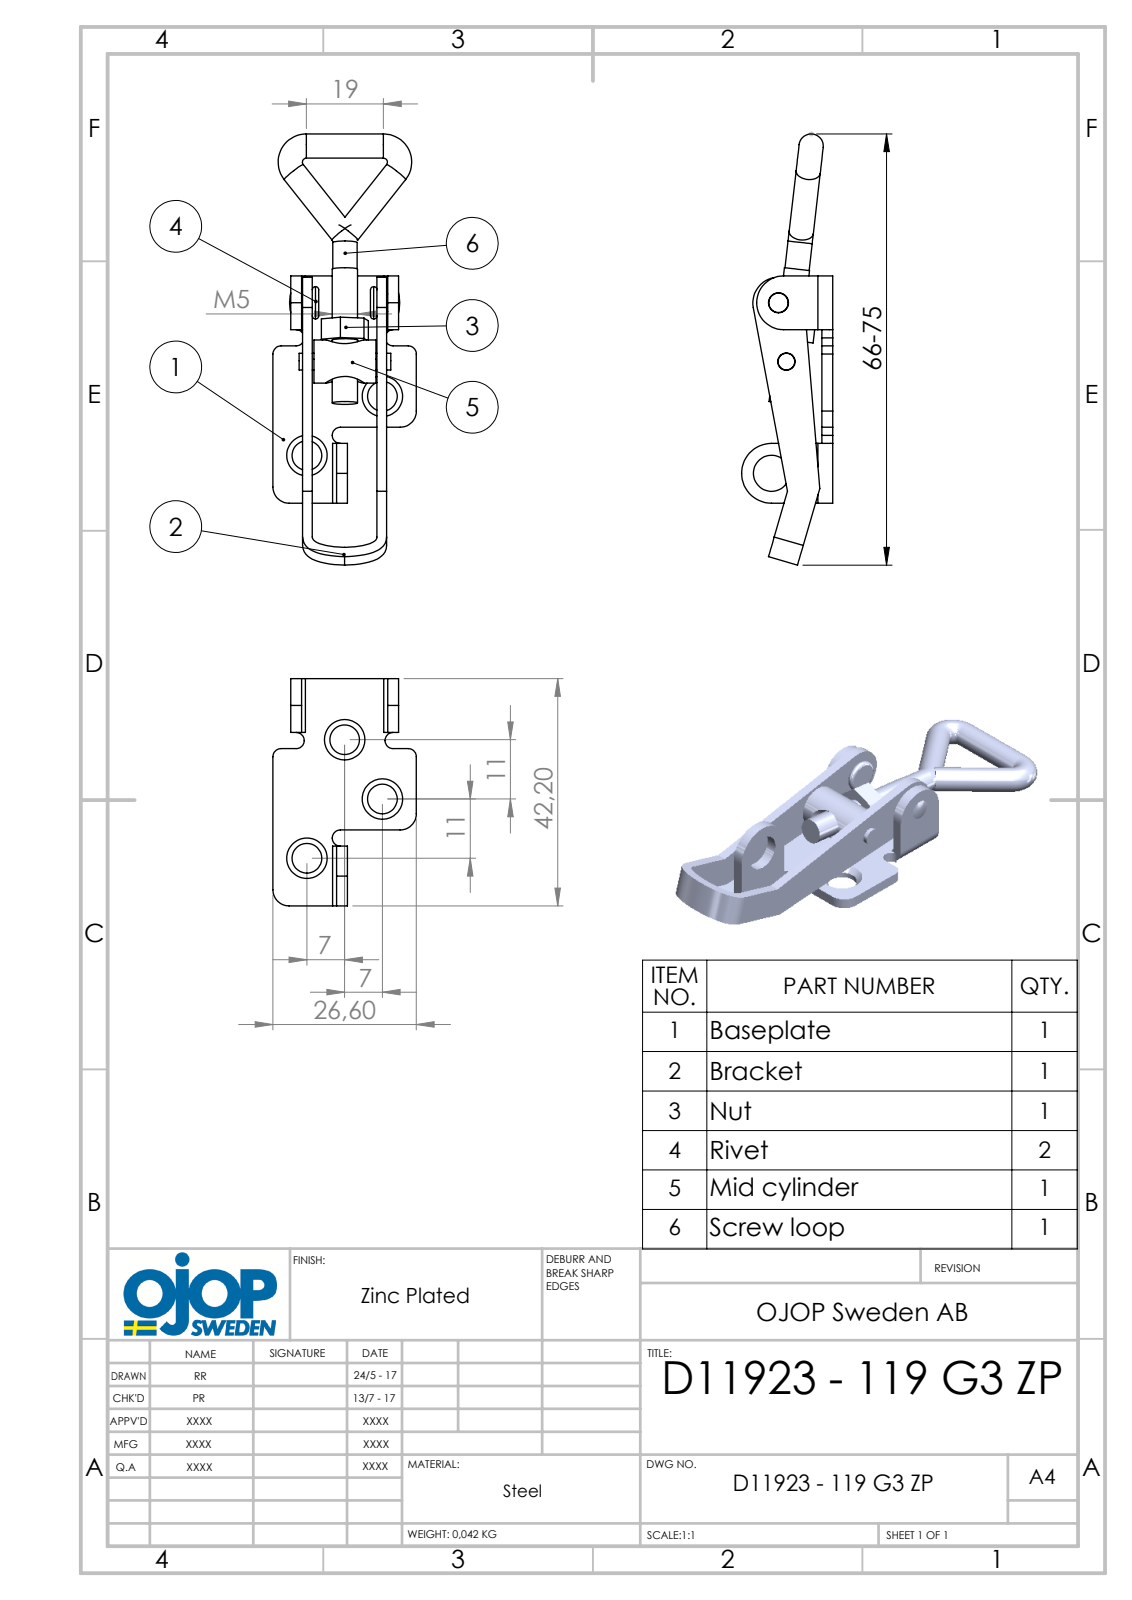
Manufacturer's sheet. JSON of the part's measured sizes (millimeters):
{"part_name": "mutter; nit; platta; skruvögla (+3 more)", "step_written_by": "SolidWorks 2015 (AUTOMOTIVE_DESIGN)", "units": "millimeters", "bodies": {"solids": 7, "faces": 163, "planar": 61, "cylindrical": 68, "other": 34}, "overall_size": [80.04, 26.6, 16.9], "volume_mm3": 5676, "surface_area_mm2": 7026, "round_holes": [[5.5, 3], [4.8, 2], [3.2, 1], [3.4, 1], [3.6, 1], [6.7, 1]], "round_bosses_or_shafts": [[4.5, 4], [8, 1], [4.7, 1], [3.3, 1], [3.1, 1]], "partial_cylinders_radius": [[1.5, 5], [0.74, 3], [2.74, 3], [3, 2], [4.75, 1], [5, 1], [5.55, 1]], "face_to_face_distances": [2, 13.8, 1.8, 12, 15.6, 16, 2.2, 15.8, 8.5, 7.5], "hole_center_spacings": [11.02, 13.01, 18.4, 20.91, 23.34, 31.68]}
